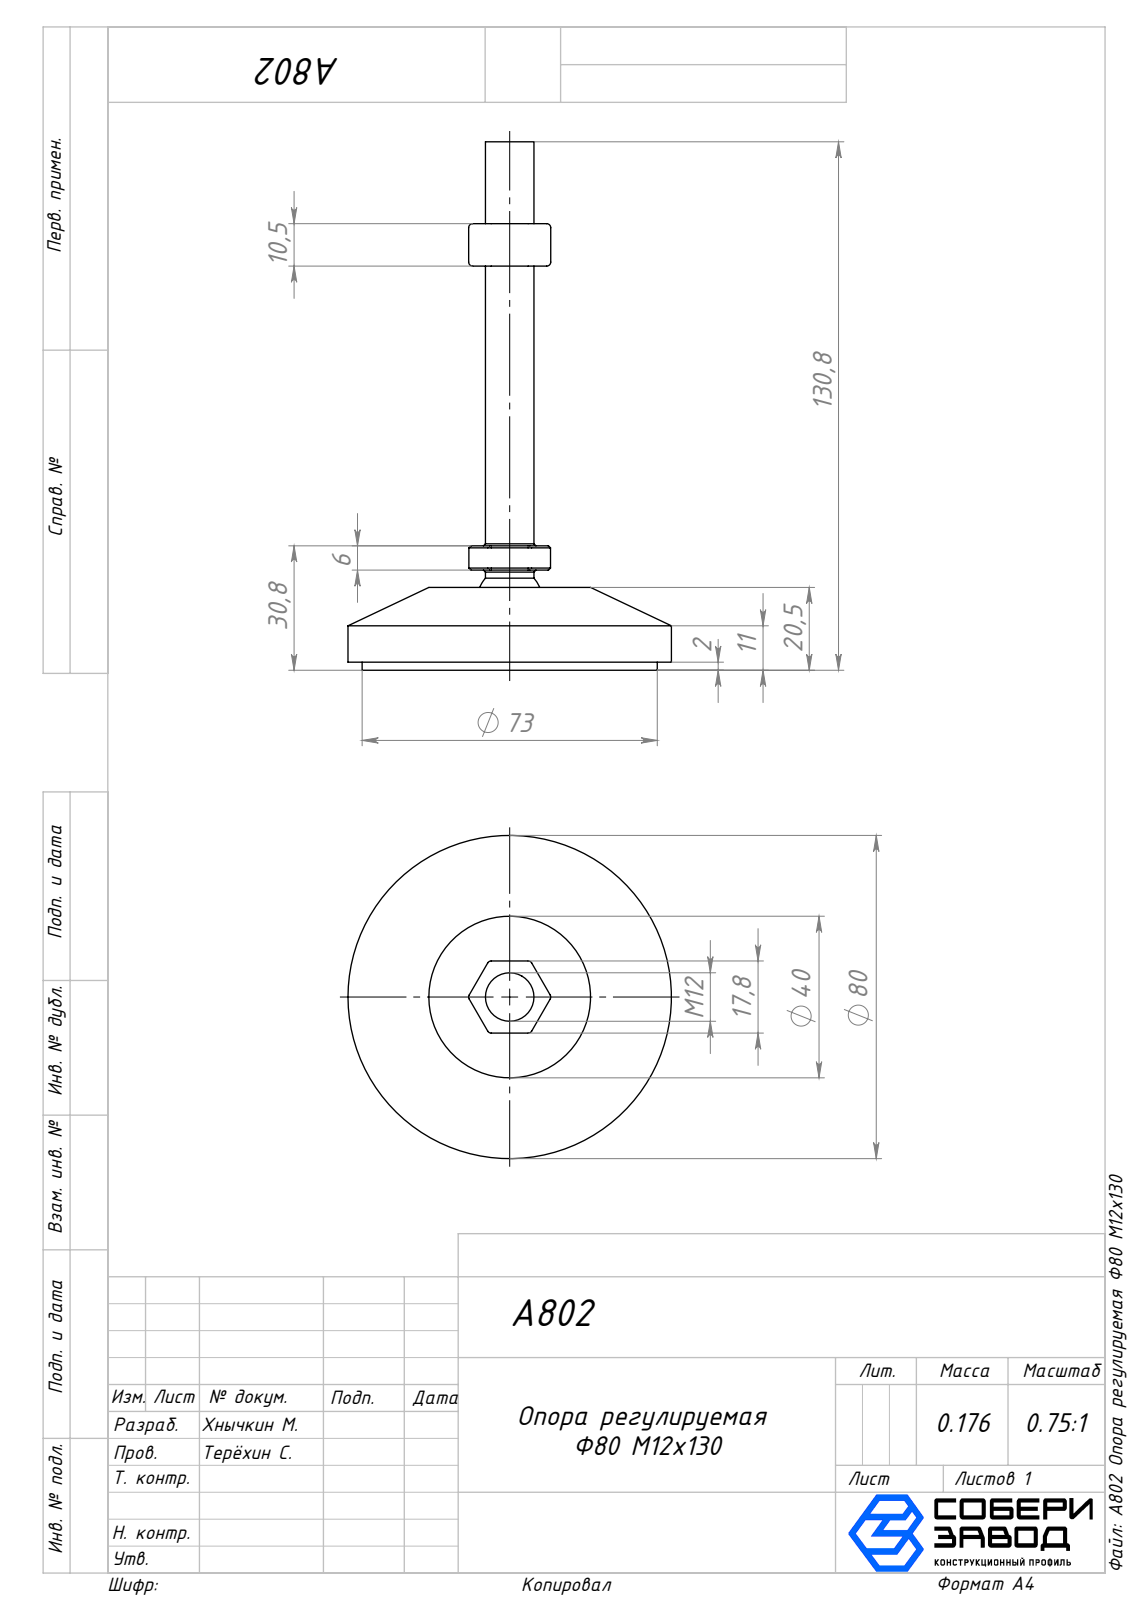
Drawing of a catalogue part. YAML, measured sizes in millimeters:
part_name: "Шарнирный вал M12_00; A802 Опора регулируемая Ф80 М12х130; Гайка М12_00; Опора_00"
step_written_by: "SolidWorks 2025 (AUTOMOTIVE_DESIGN)"
units: millimeters
bodies: {solids: 3, faces: 110, planar: 32, cylindrical: 38, other: 40}
overall_size: [130.79, 80, 80]
volume: 96947
surface_area: 20061
round_holes:
  - {diameter: 10, count: 1}
  - {diameter: 16, count: 1}
round_bosses_or_shafts:
  - {diameter: 80, count: 1}
  - {diameter: 73, count: 1}
  - {diameter: 12, count: 1}
partial_cylinders:
  - {radius: 1, count: 24}
face_to_face_distances: [20.5, 2, 18.5, 17.8, 17.86, 130.79, 128.79, 110.29, 30.79, 28.79]
